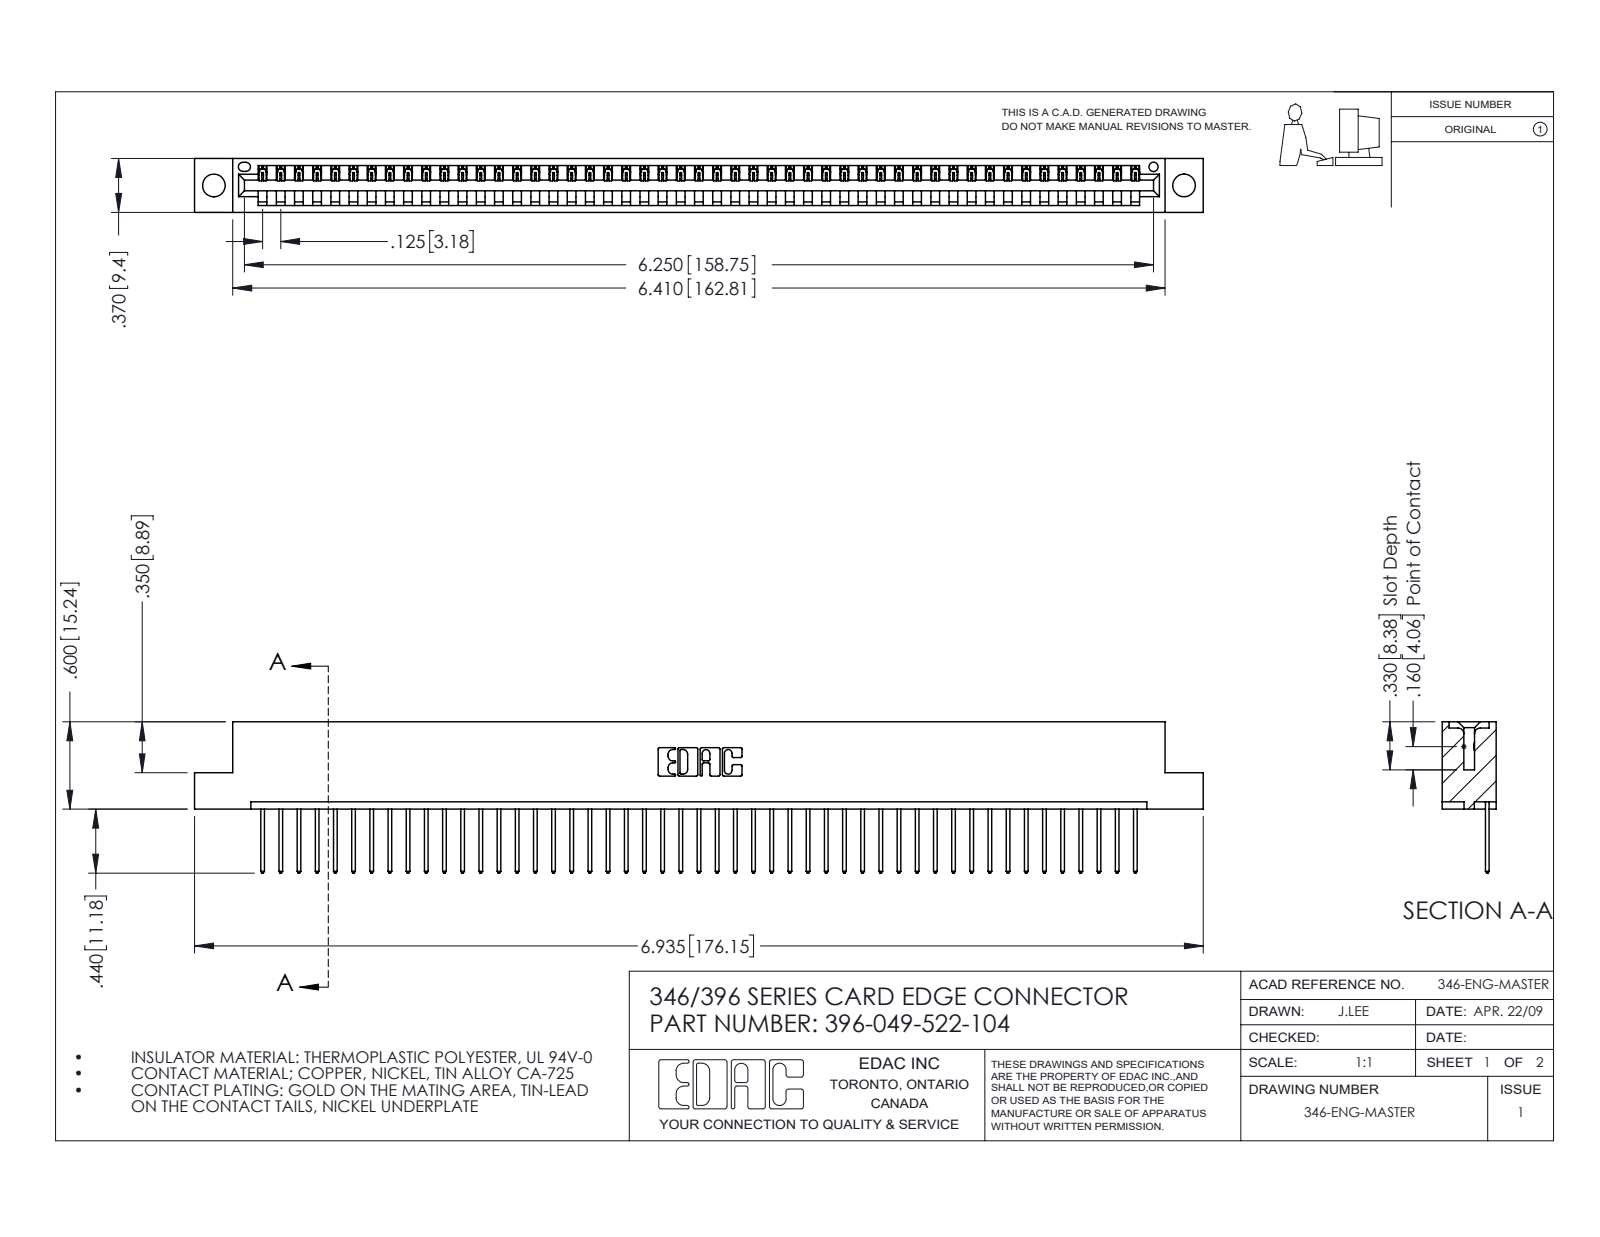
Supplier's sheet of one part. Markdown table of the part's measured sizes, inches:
| quantity | value |
| --- | --- |
| part name | 346 Part_Flush Mounting Lugs - 0.156 Dia-TH; 345-292-001_345-293-122; 396-049-522-104 |
| STEP written by | SolidWorks 2016 (CONFIG_CONTROL_DESIGN) |
| units | inches |
| bodies | 50 solids, 2964 faces (2036 planar, 928 cylindrical, 0 other) |
| overall size | 6.935 × 1.04 × 0.37 |
| volume | 1.027 in³ |
| surface area | 32.7 in² |
| round holes (diameter × count) | 0.156 × 2, 0.064 × 1 |
| partial cylindrical surfaces (radius × count) | 0.006 × 98, 0.01 × 98, 0.01 × 22, 0.007 × 6, 0.031 × 6, 0.026 × 3, 0.031 × 2, 0.04 × 2 |
| main face-to-face distances | 0.048, 0.322, 0.37, 0.25, 0.072, 0.298, 0.025, 0.148, 0.222, 0.1 |
| hole center spacings | 0.246, 6.461, 6.67 |
